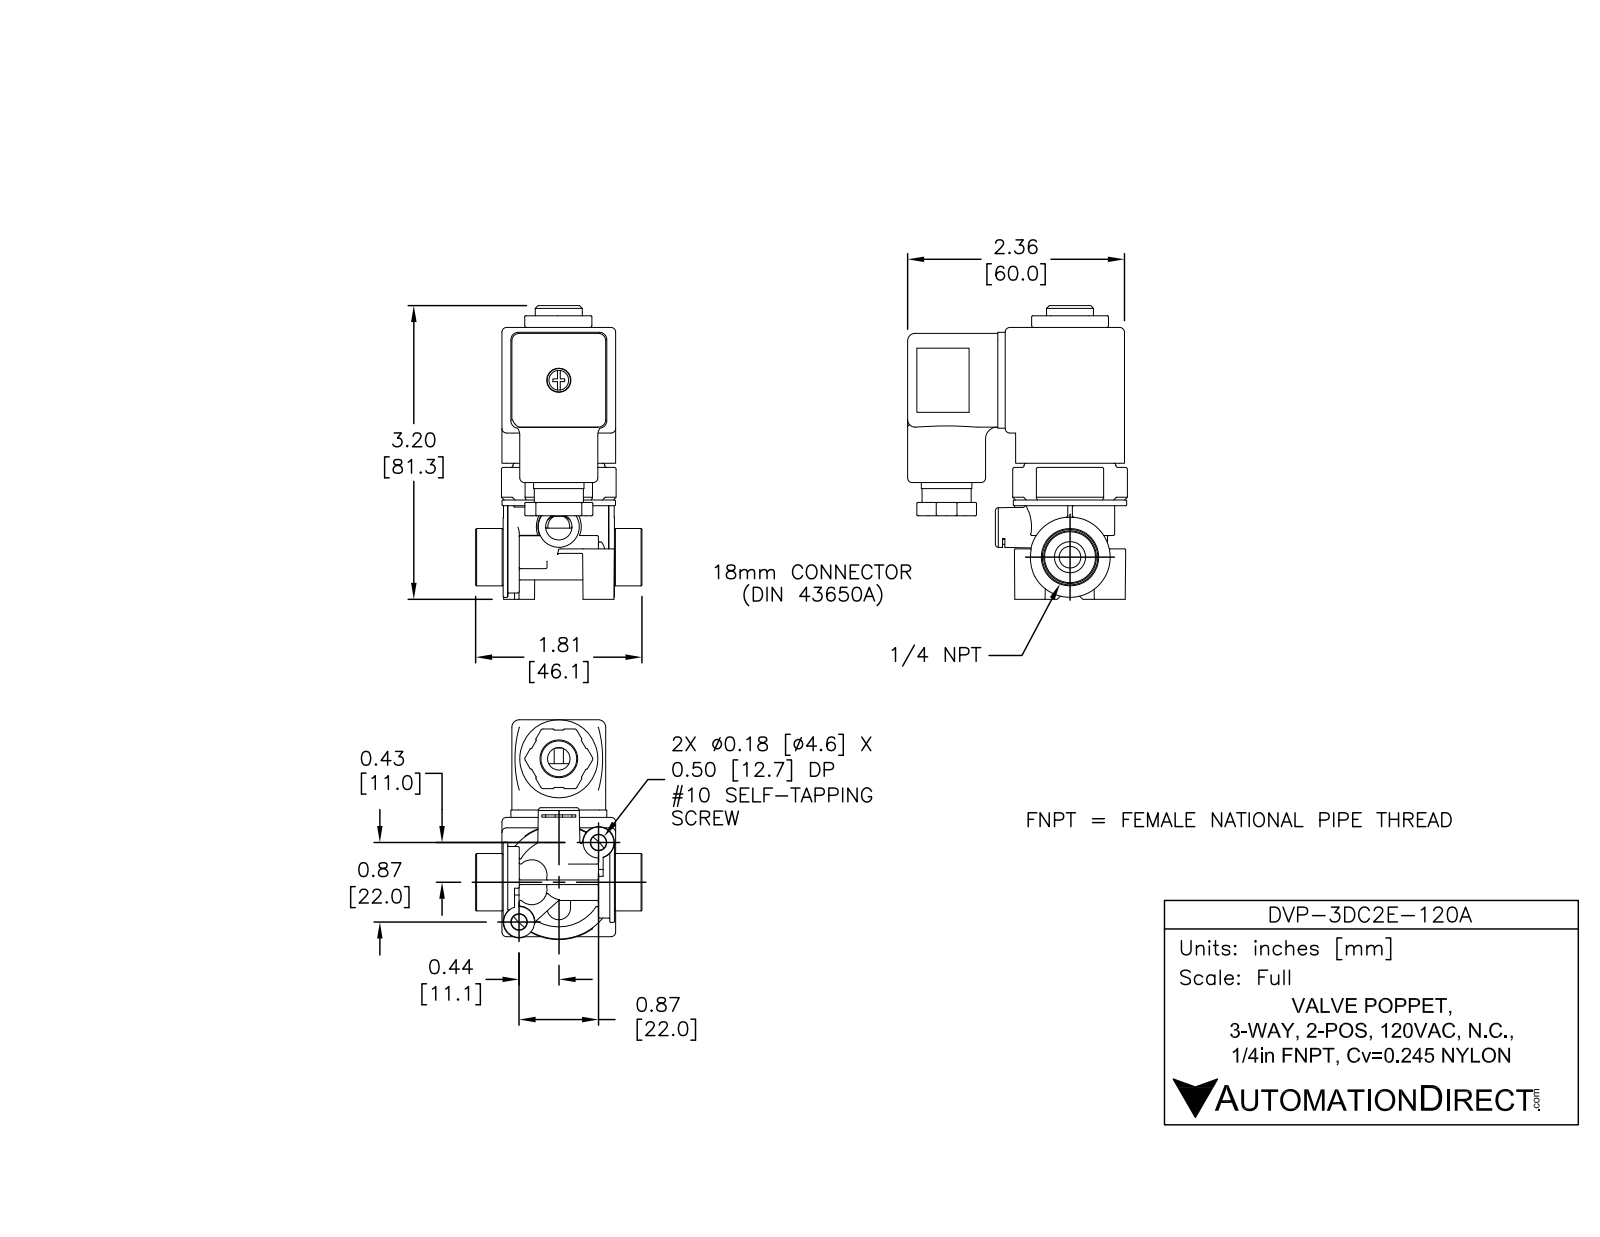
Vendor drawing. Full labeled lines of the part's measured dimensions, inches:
Part name (STEP PRODUCT): DVP-3DC2E-120A
STEP written by: SolidWorks 2015 (AUTOMOTIVE_DESIGN)
Units: inches
Bodies: 7 solids, 1850 faces (809 planar, 362 cylindrical, 679 other)
Overall size (bounding box): 3.204 × 2.395 × 1.813
Volume: 3.912 in³ · Surface area: 55.24 in²
Round holes (diameter × count): ⌀0.06 ×2, ⌀0.236 ×2, ⌀0.093 ×1, ⌀0.095 ×1, ⌀0.102 ×1, ⌀0.12 ×1, ⌀0.137 ×1, ⌀0.203 ×1, ⌀0.245 ×1, ⌀0.25 ×1, ⌀0.263 ×1, ⌀0.287 ×1
Round bosses / shafts (diameter × count): ⌀0.29 ×2, ⌀1.236 ×1, ⌀1 ×1, ⌀0.972 ×1, ⌀0.922 ×1, ⌀0.89 ×1, ⌀0.875 ×1, ⌀0.85 ×1
Partial cylindrical surfaces — rounded edges, fillets, slot ends (radius × count): R0.01 ×75, R0.015 ×38, R0.05 ×21, R0.02 ×12, R0.08 ×12, R0.026 ×6, R0.03 ×6, R0.04 ×4
Main face-to-face distances: 1.083, 1.24, 0.048, 0.157, 0.925, 1.416, 1.48, 0.109, 1.131, 0.974
Hole centre spacings: 0.281, 0.283, 1.062, 1.343, 1.345, 1.612, 1.626, 2.184
